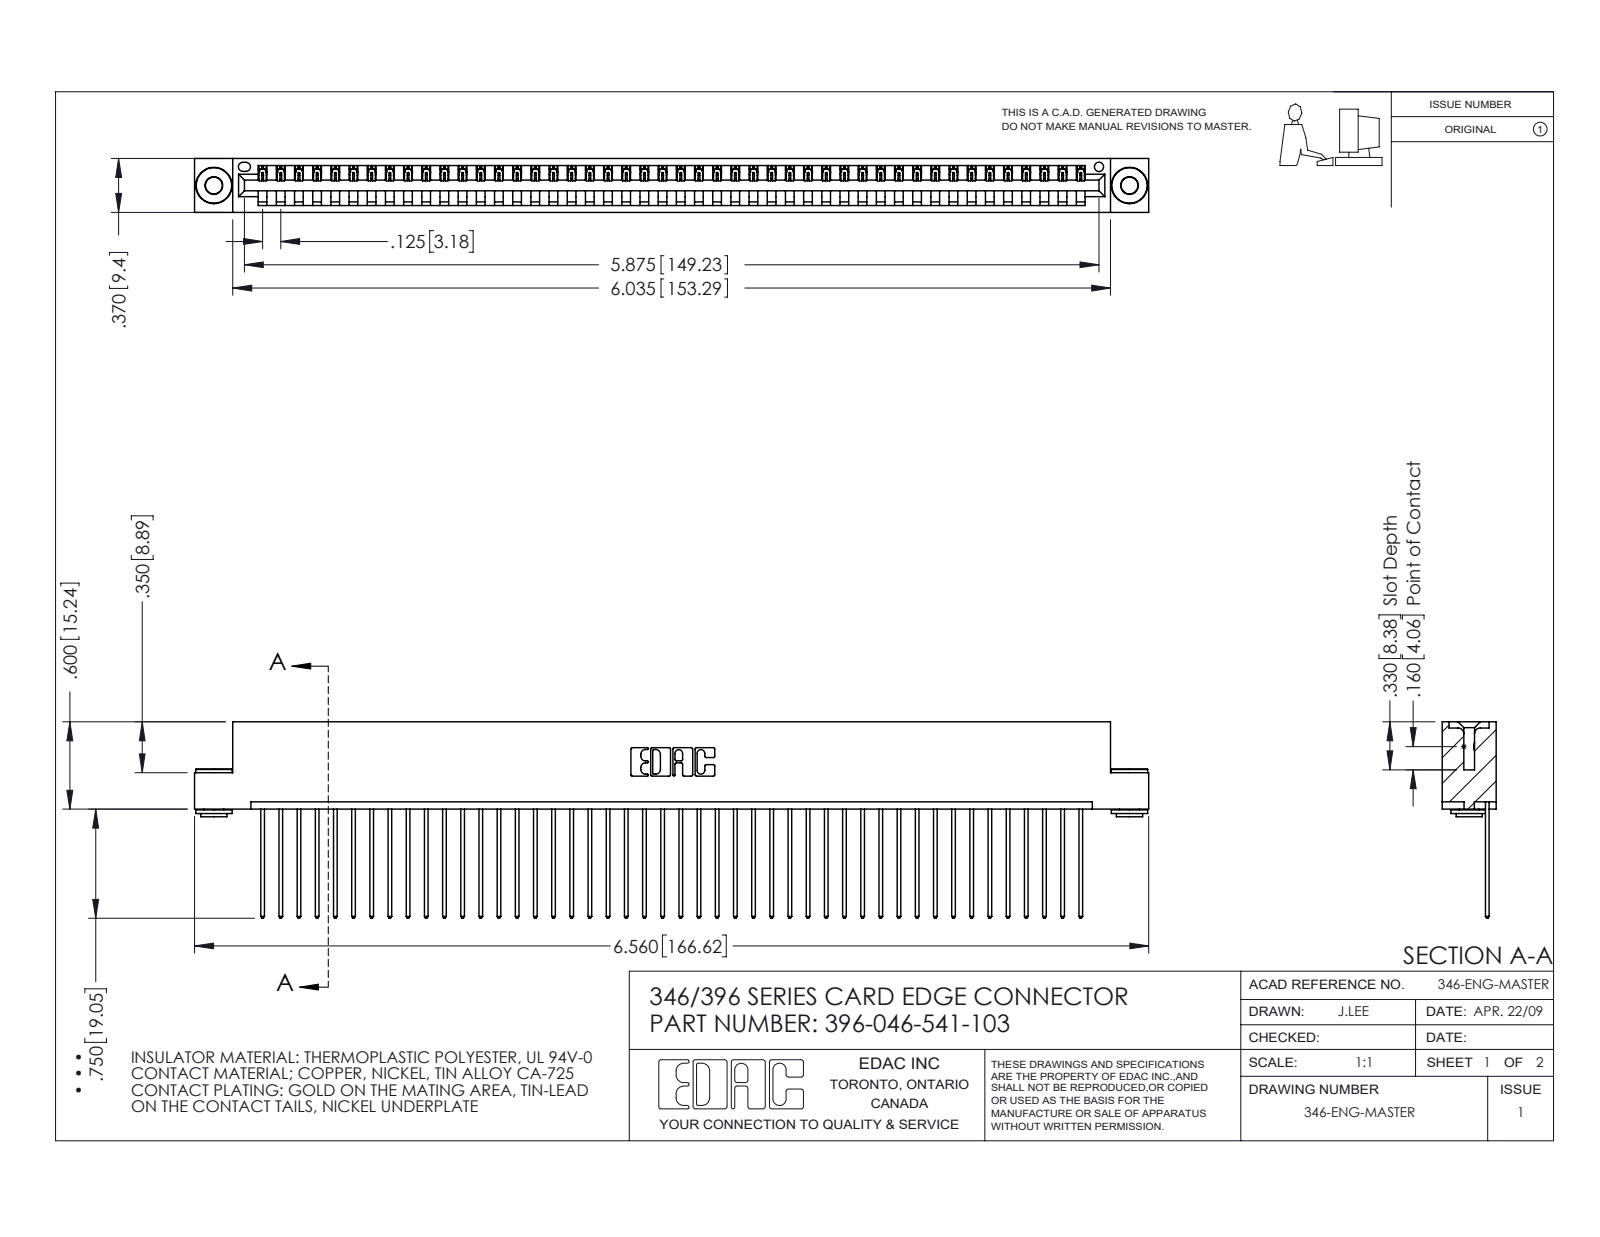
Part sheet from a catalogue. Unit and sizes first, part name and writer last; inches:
Units: inches
Overall size (bounding box): 6.56 × 1.35 × 0.37
Round holes (diameter × count): ⌀0.116 ×2, ⌀0.156 ×2, ⌀0.064 ×1
Round bosses / shafts (diameter × count): ⌀0.25 ×2, ⌀0.18 ×2, ⌀0.136 ×2
Partial cylindrical surfaces — rounded edges, fillets, slot ends (radius × count): R0.006 ×92, R0.01 ×92, R0.01 ×22, R0.007 ×6, R0.031 ×6, R0.026 ×3, R0.031 ×2, R0.04 ×2
Main face-to-face distances: 0.048, 0.322, 0.37, 0.25, 0.025, 0.072, 0.298, 0.148, 0.222, 0.1
Hole centre spacings: 0.246, 6.086, 6.295
Volume: 0.985 in³ · Surface area: 33.1 in²
Bodies: 49 solids, 2828 faces (1926 planar, 894 cylindrical, 8 other)
Part name (STEP PRODUCT): 345-292-001_345-293-141; 345-250-002_345-250-002-102; 396-046-541-103; 346 Part_Flush Mounting Lugs - 0.156 Dia-TH
STEP written by: SolidWorks 2016 (CONFIG_CONTROL_DESIGN)
